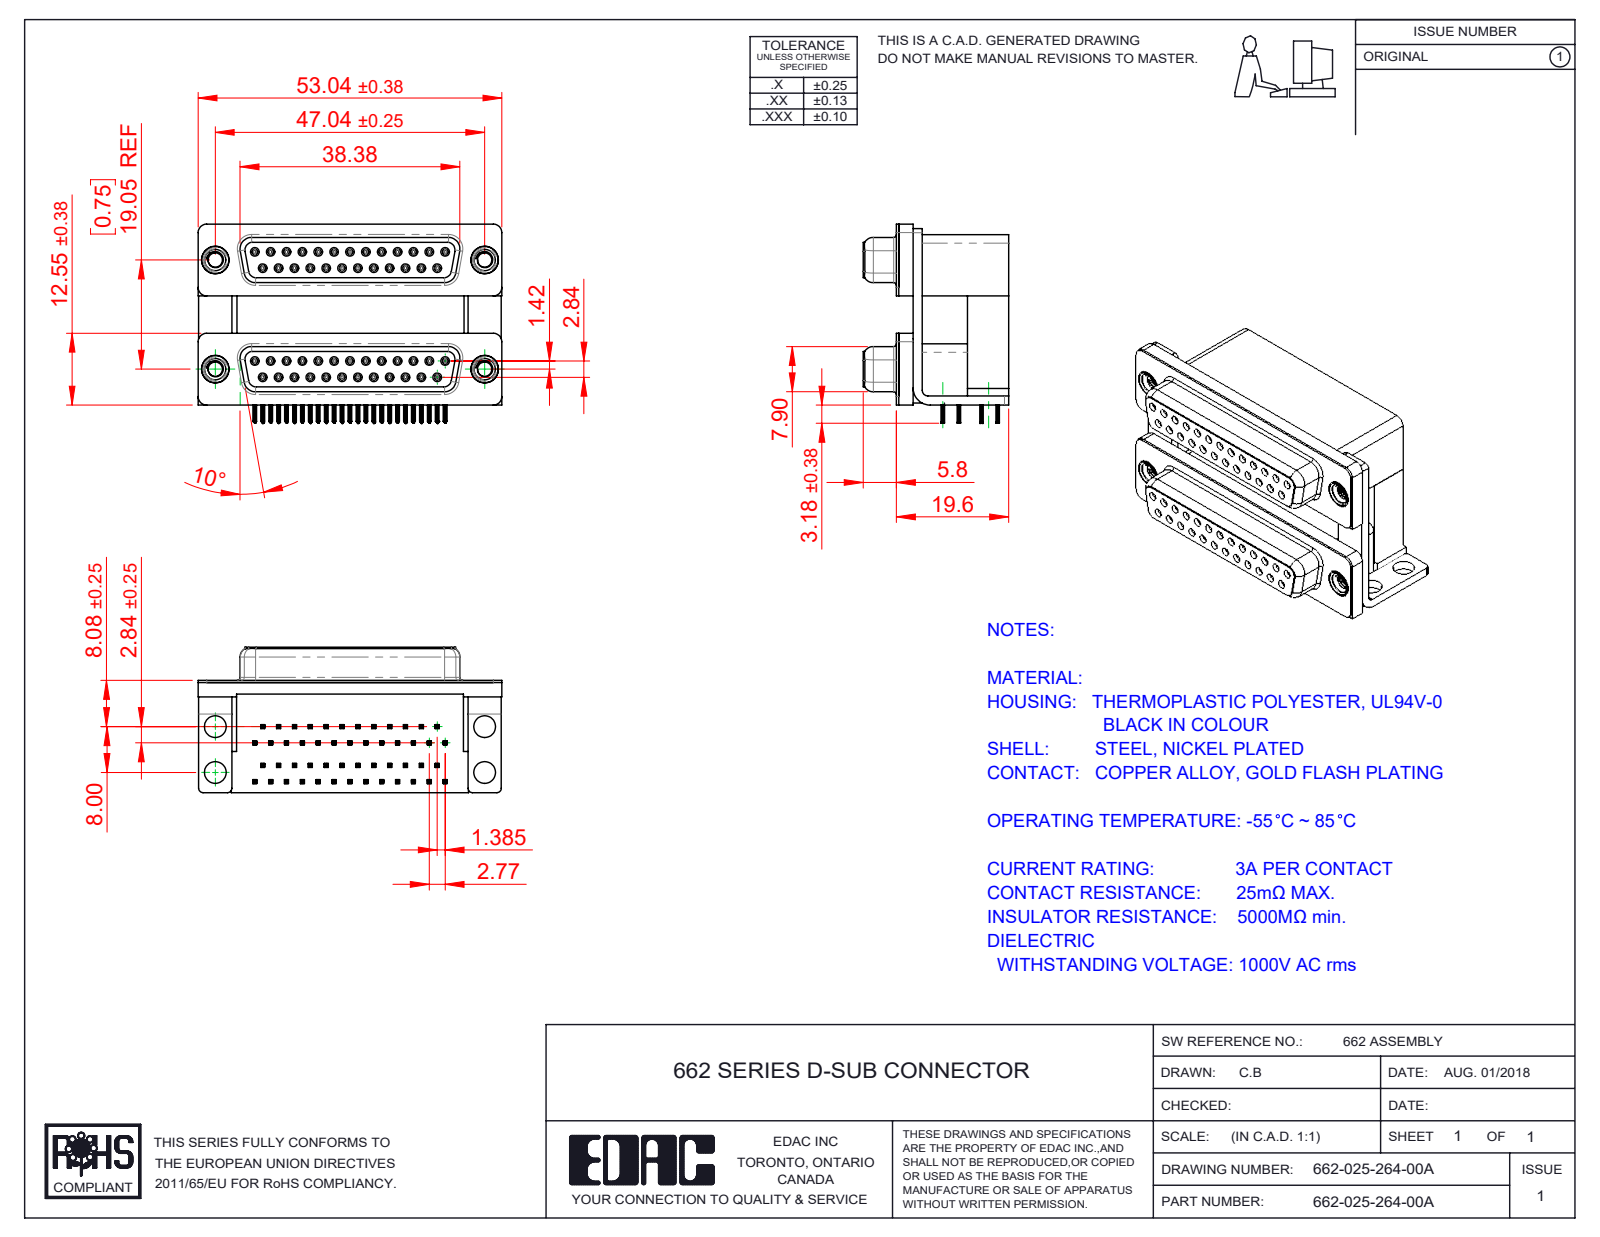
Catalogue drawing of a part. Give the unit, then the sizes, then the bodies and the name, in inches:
Units: inches
Overall size (bounding box): 2.088 × 1.369 × 1
Round holes (diameter × count): ⌀0.031 ×50, ⌀0.035 ×50, ⌀0.098 ×4, ⌀0.138 ×4, ⌀0.15 ×4, ⌀0.157 ×4, ⌀0.189 ×4, ⌀0.197 ×4
Round bosses / shafts (diameter × count): ⌀0.047 ×50, ⌀0.193 ×4, ⌀0.187 ×4, ⌀0.154 ×4
Partial cylindrical surfaces — rounded edges, fillets, slot ends (radius × count): R0.004 ×400, R0.006 ×200, R0.014 ×100, R0.013 ×50, R0.011 ×24, R0.053 ×16, R0.059 ×14, R0.02 ×8
Main face-to-face distances: 0.756, 0.75, 0.472, 0.016, 0.283, 0.244, 0.421, 0.098, 0.657, 0.374
Hole centre spacings: 0.124, 0.109, 0.218, 0.436, 0.327, 0.198, 0.545, 0.294
Volume: 1.453 in³ · Surface area: 40.01 in²
Bodies: 61 solids, 7796 faces (3576 planar, 1812 cylindrical, 2408 other)
Part name (STEP PRODUCT): 662 Housing Lower_25 Contacts; 662 Threaded Rivet_M3; 662 Housing Spacer_25 Contacts M; 662 Contact Bottom Upper_M (+7 more)
STEP written by: SolidWorks 2020 (CONFIG_CONTROL_DESIGN)
